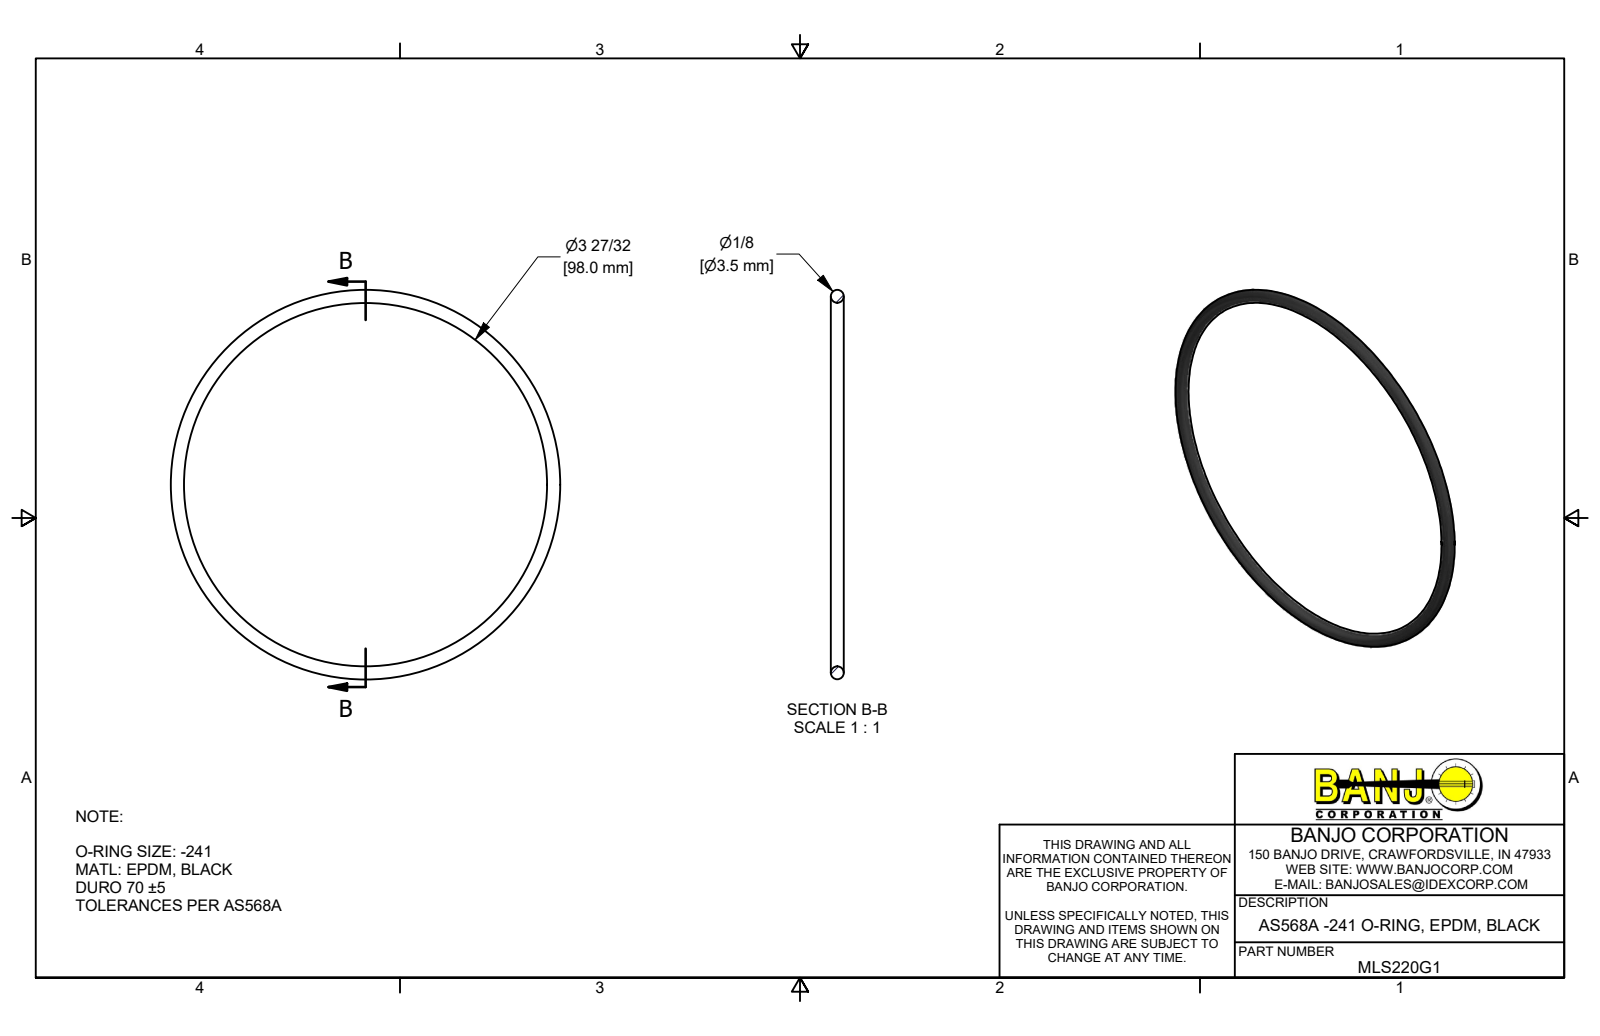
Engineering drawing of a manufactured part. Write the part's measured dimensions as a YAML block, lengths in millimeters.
part_name: "MLS220G1"
step_written_by: "Autodesk Inventor 2019 (AUTOMOTIVE_DESIGN)"
units: millimeters
bodies: {solids: 1, faces: 1, planar: 0, cylindrical: 0, other: 1}
overall_size: [105.1, 105.1, 3.5]
volume: 3130
surface_area: 3539
